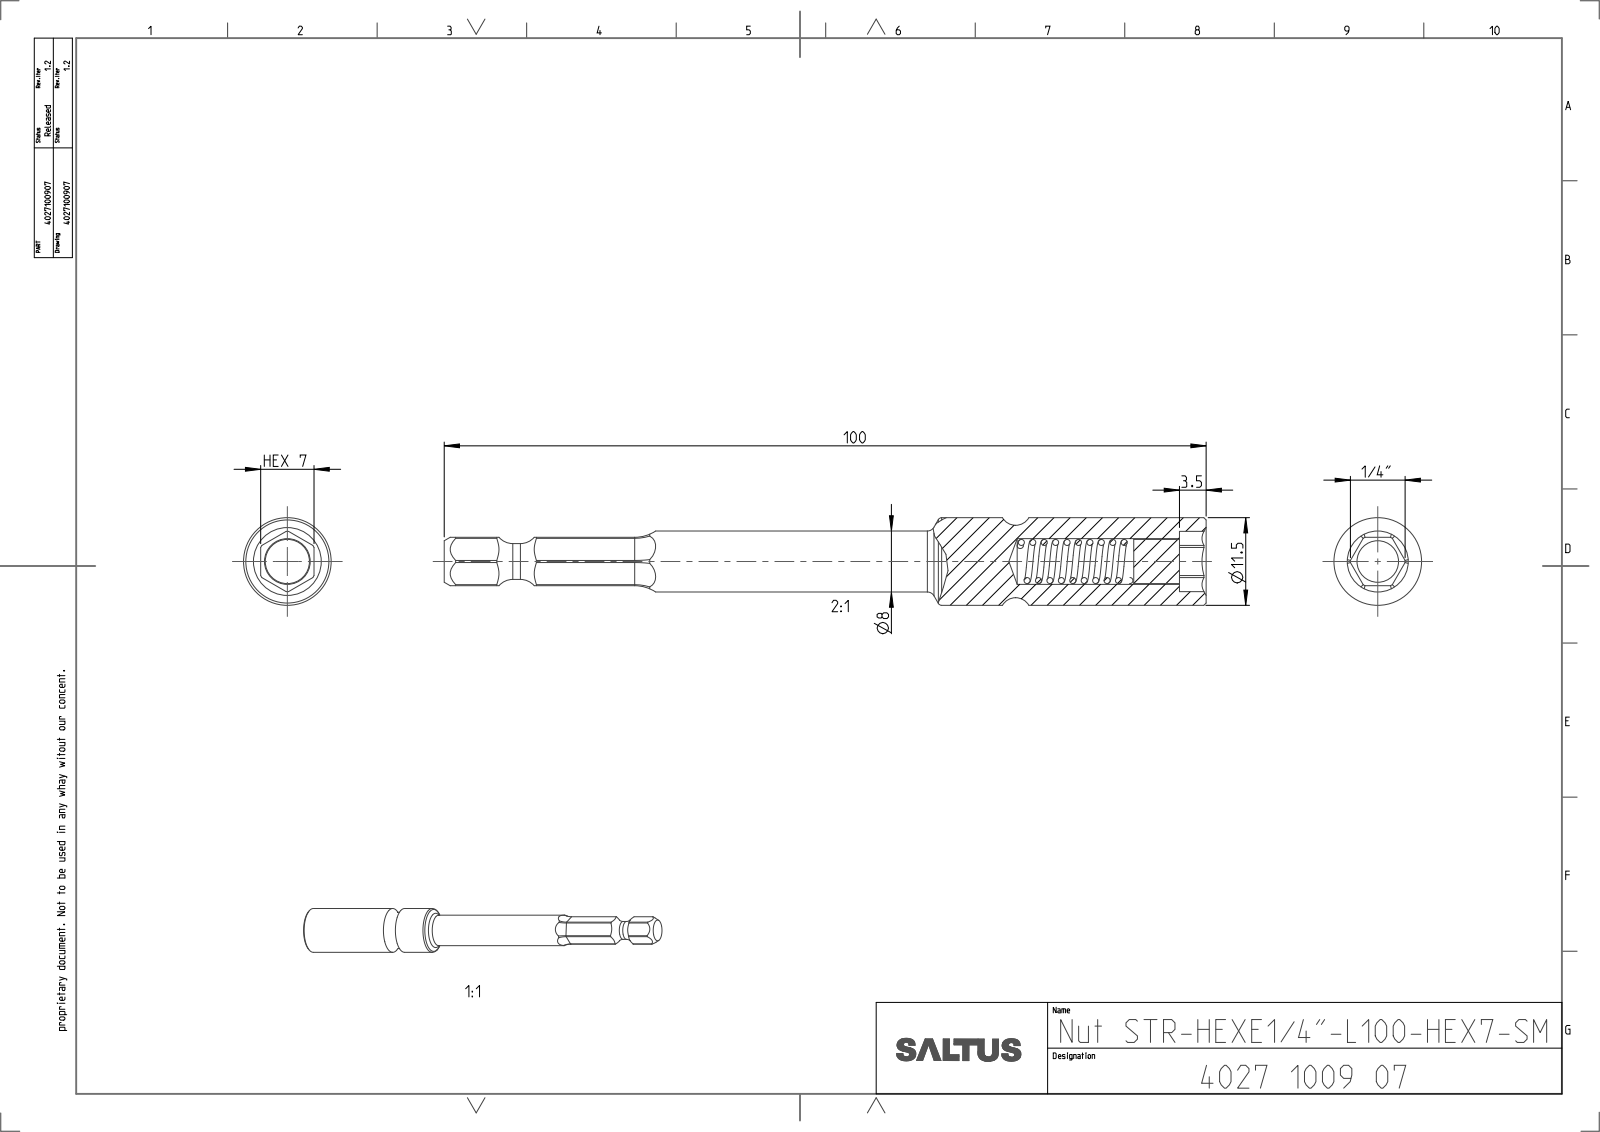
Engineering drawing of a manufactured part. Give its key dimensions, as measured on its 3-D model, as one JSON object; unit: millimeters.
{"part_name": "4027100907", "step_written_by": "CREO PARAMETRIC BY PTC INC, 2022414 (CONFIG_CONTROL_DESIGN)", "units": "millimeters", "bodies": {"solids": 3, "faces": 93, "planar": 25, "cylindrical": 36, "other": 32}, "overall_size": [100, 11.5, 11.5], "volume_mm3": 5829, "surface_area_mm2": 3979, "round_holes": [[6, 1]], "round_bosses_or_shafts": [[11.5, 1], [8, 1], [5.8, 1], [4.7, 1]], "partial_cylinders_radius": [[5, 6], [3.59, 1], [3.96, 1]], "face_to_face_distances": [6.34, 6.36, 7, 3.5, 6, 9.5, 90.5, 96.5, 100]}
